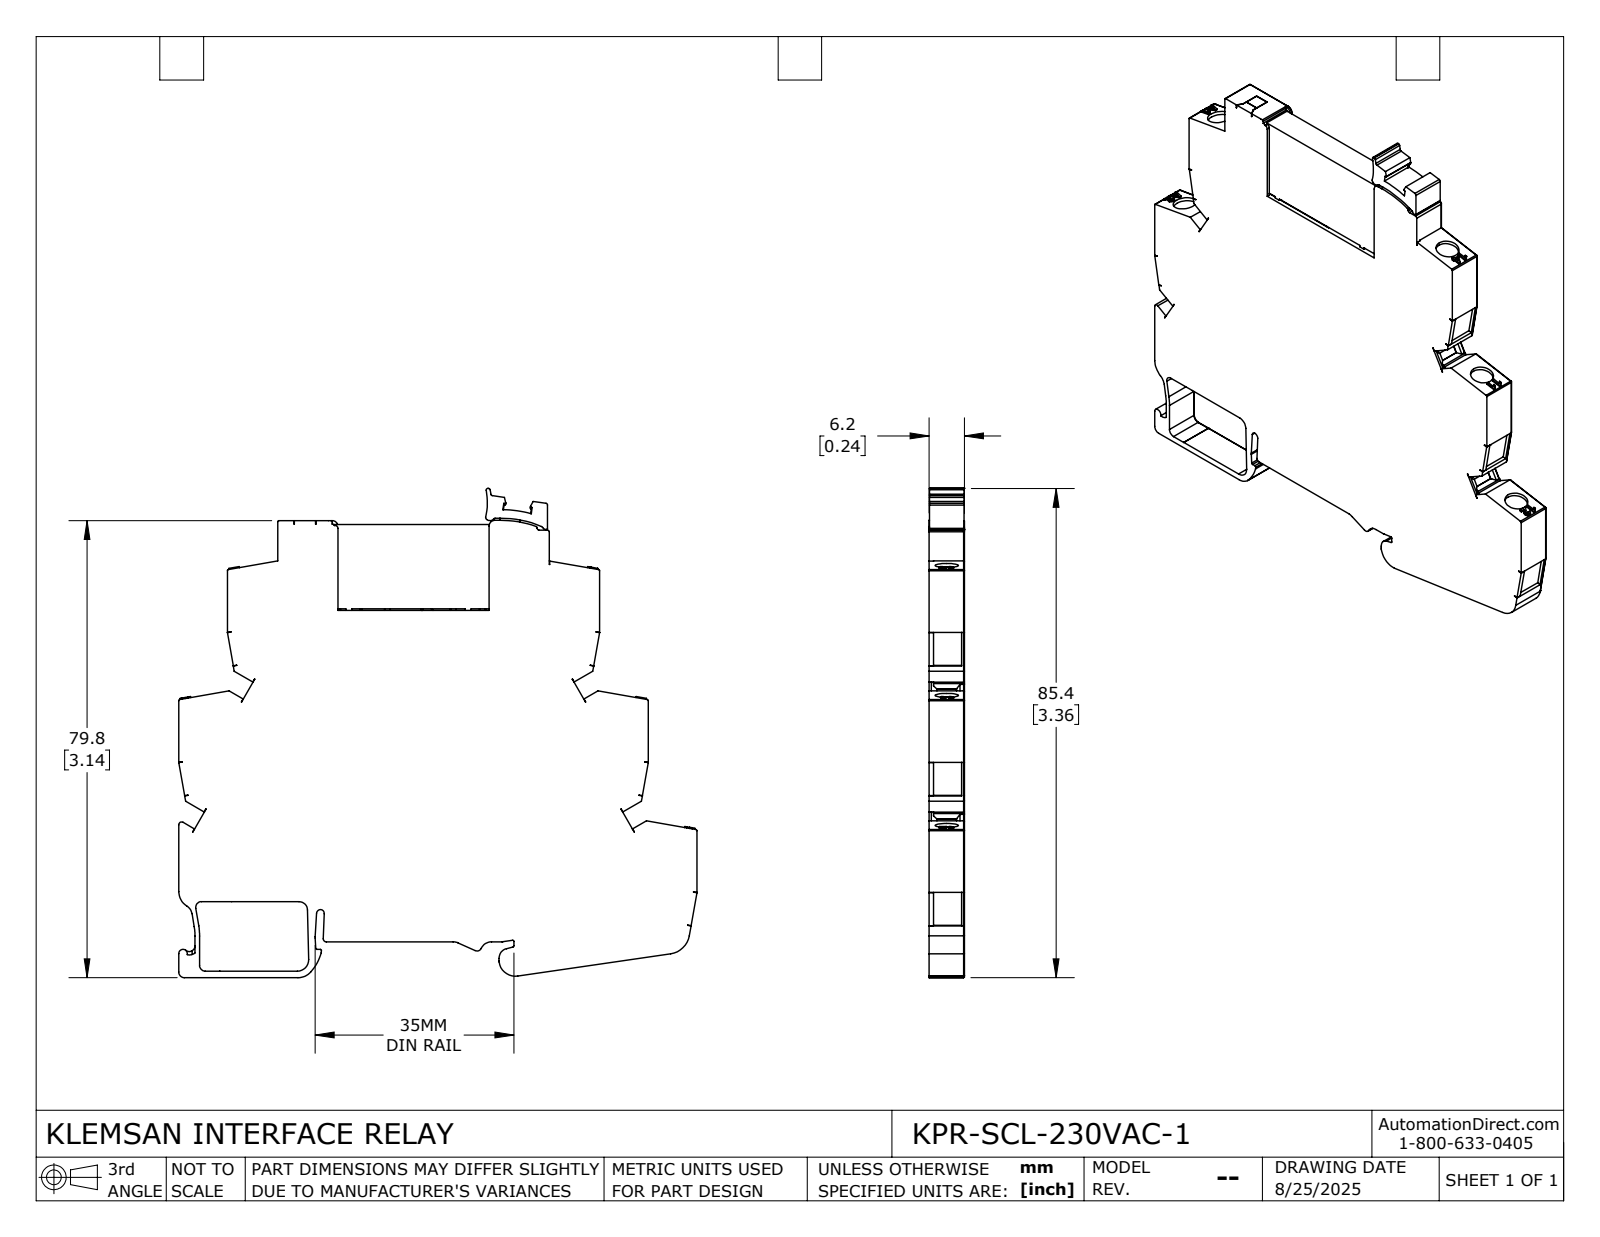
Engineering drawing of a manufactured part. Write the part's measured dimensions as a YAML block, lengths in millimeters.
part_name: "KPR-SCL-230VAC-1"
step_written_by: "SolidWorks 2024 (CONFIG_CONTROL_DESIGN)"
units: millimeters
bodies: {solids: 1, faces: 764, planar: 578, cylindrical: 148, other: 38}
overall_size: [90.49, 85.41, 6.2]
volume: 33364
surface_area: 14579
round_holes:
  - {diameter: 4.05, count: 5}
round_bosses_or_shafts:
  - {diameter: 0.4, count: 2}
partial_cylinders:
  - {radius: 0.2, count: 22}
  - {radius: 0.3, count: 11}
  - {radius: 0.1, count: 10}
  - {radius: 1, count: 9}
  - {radius: 0.5, count: 7}
  - {radius: 0.4, count: 5}
  - {radius: 0.9, count: 5}
  - {radius: 2, count: 5}
face_to_face_distances: [6.2, 0.6, 5.6, 5, 0.5, 72.82, 58.12, 14.7, 8.49, 8.5]
hole_center_spacings: [12.3, 12.32, 12.33, 24.61]
